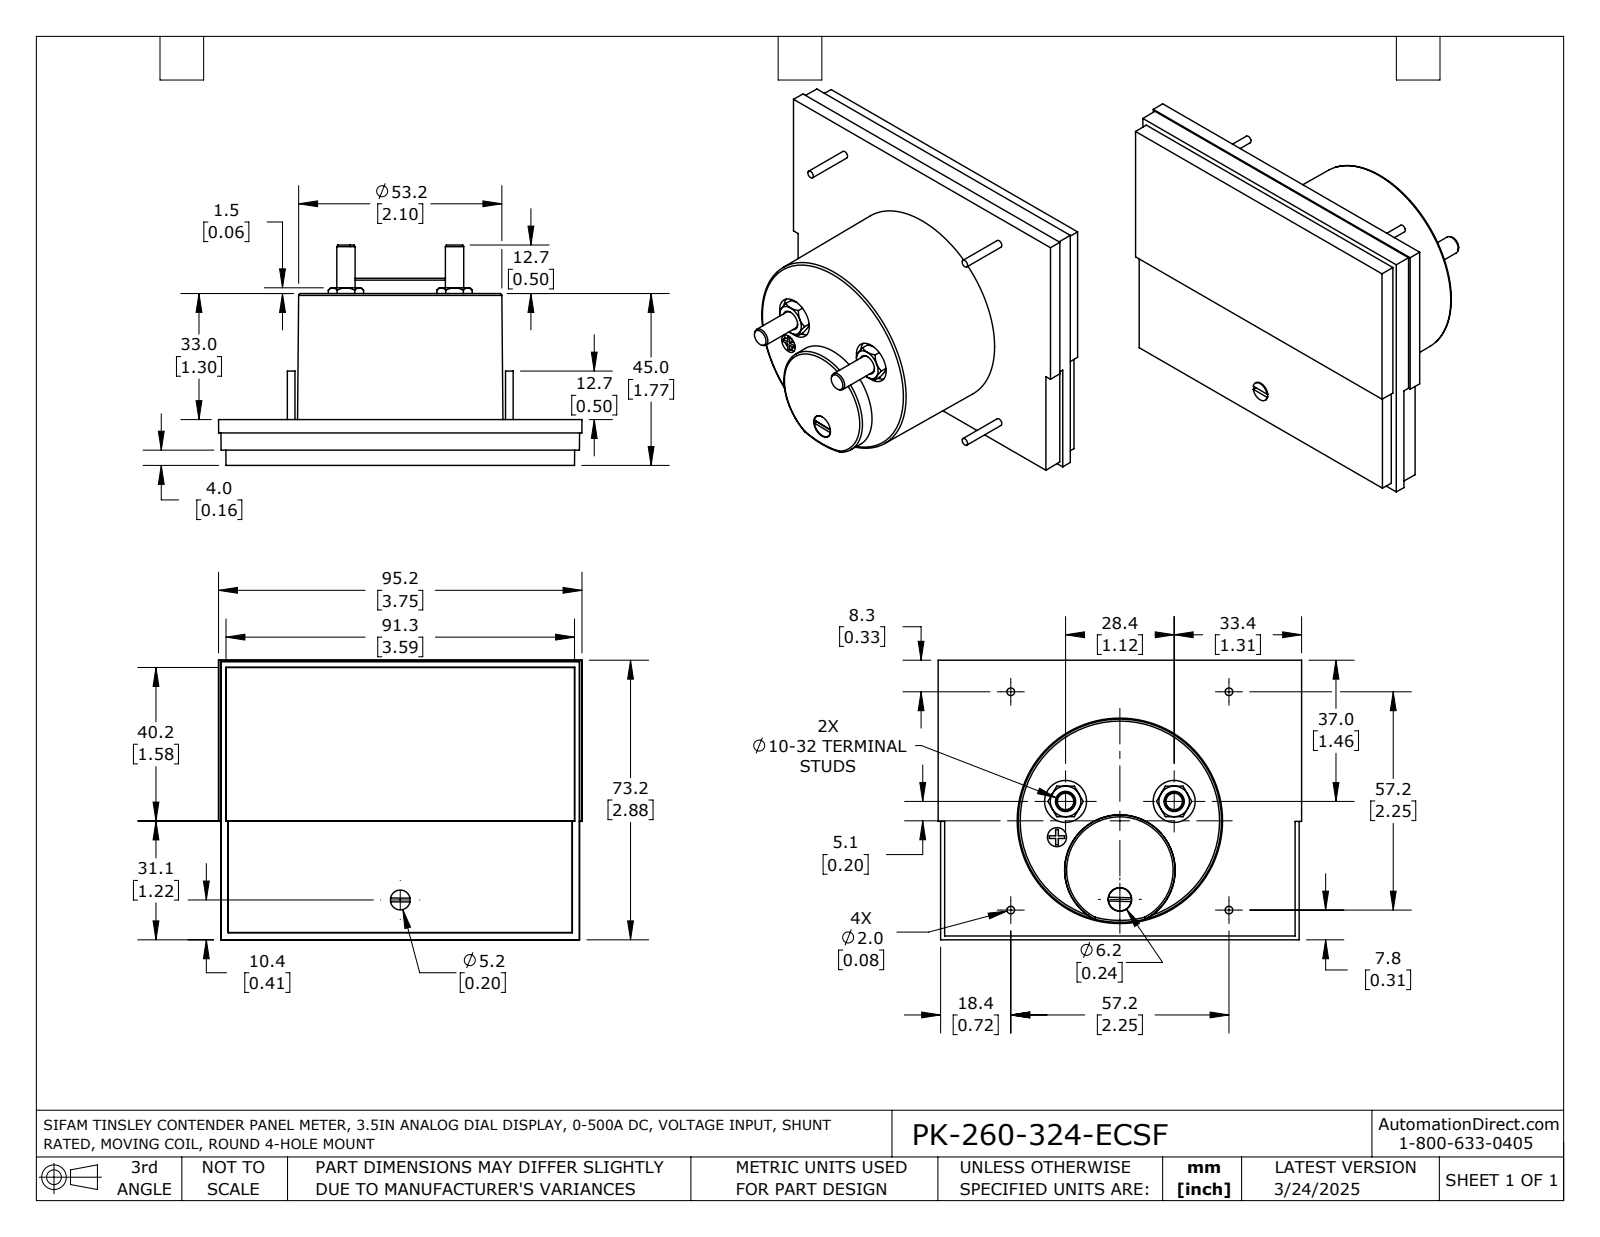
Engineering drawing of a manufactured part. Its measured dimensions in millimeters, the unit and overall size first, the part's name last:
Units: millimetres
Overall size (bounding box): 95.2 × 73.2 × 57.7
Round holes (diameter × count): ⌀11 ×2, ⌀5 ×1, ⌀6.2 ×1
Round bosses / shafts (diameter × count): ⌀2 ×4, ⌀4.8 ×2, ⌀6 ×1, ⌀5.2 ×1
Partial cylindrical surfaces — rounded edges, fillets, slot ends (radius × count): R2.5 ×1
Main face-to-face distances: 12, 0.8, 11.3, 45, 33, 44.2, 4, 1.9, 8, 37
Hole centre spacings: 29.3, 9.6, 23.2, 28.4, 32.1
Volume: 154 800 mm³ · Surface area: 24 770 mm²
Bodies: 1 solid, 163 faces (76 planar, 31 cylindrical, 56 other)
Part name (STEP PRODUCT): PK-260-324-ECSF
STEP written by: SolidWorks 2021 (AUTOMOTIVE_DESIGN)
